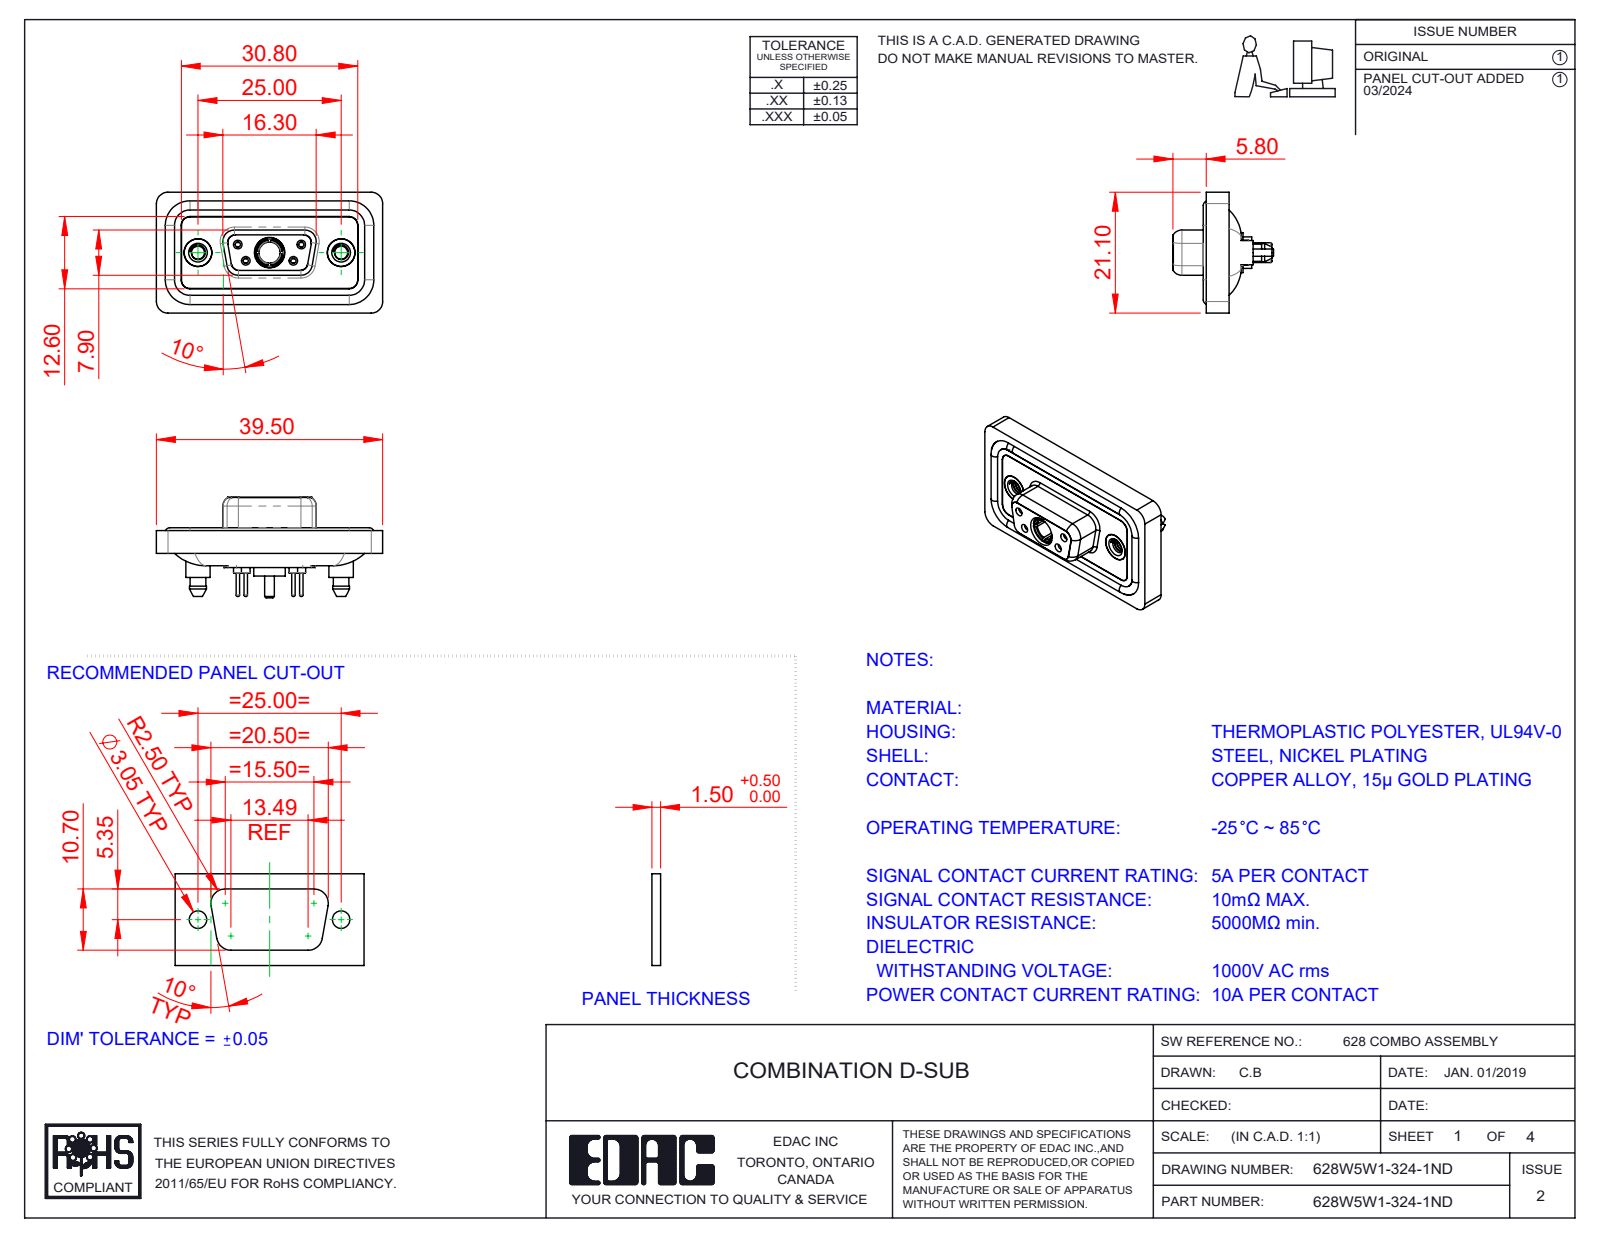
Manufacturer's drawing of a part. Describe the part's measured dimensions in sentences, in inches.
The part is named "628Combo Contact Row 2_24; 628Combo Shell Front_09 Contacts; 628Combo Shell Rear_09 Contacts; 628Combo Threaded Boardlock_D (+5 more)". Its 3-D file was written by "SolidWorks 2023 (CONFIG_CONTROL_DESIGN)". It is 13 solids with 746 faces: 210 planar, 335 cylindrical and 201 other. Overall it measures 1.555 by 0.831 by 0.691 inches. Its volume is 0.298 cubic inches and its surface area 12.34 square inches. Round holes: 4 of diameter 0.035, 4 of diameter 0.043, 4 of diameter 0.059, 4 of diameter 0.079, 3 of diameter 0.191, 2 of diameter 0.063, 2 of diameter 0.067, 2 of diameter 0.089, 2 of diameter 0.157, 2 of diameter 0.159, 2 of diameter 0.197, 1 of diameter 0.146. Round bosses or shafts: 6 of diameter 0.063, 4 of diameter 0.087, 4 of diameter 0.024, 2 of diameter 0.213, 2 of diameter 0.195, 2 of diameter 0.189, 2 of diameter 0.167, 1 of diameter 0.217. Partial cylindrical surfaces (rounded edges, fillets, slot ends): 24 of radius 0.059, 18 of radius 0.079, 10 of radius 0.063, 8 of radius 0.053, 4 of radius 0.01, 4 of radius 0.02, 4 of radius 0.024, 4 of radius 0.026. The main face-to-face distances are 0.016, 0.114, 0.071, 0.043, 0.063, 0.02, 0.222, 0.293, 0.211, 0.142. The hole center spacings are 0.124, 0.225, 0.28, 0.492, 0.713, 0.173, 0.173, 0.327.
